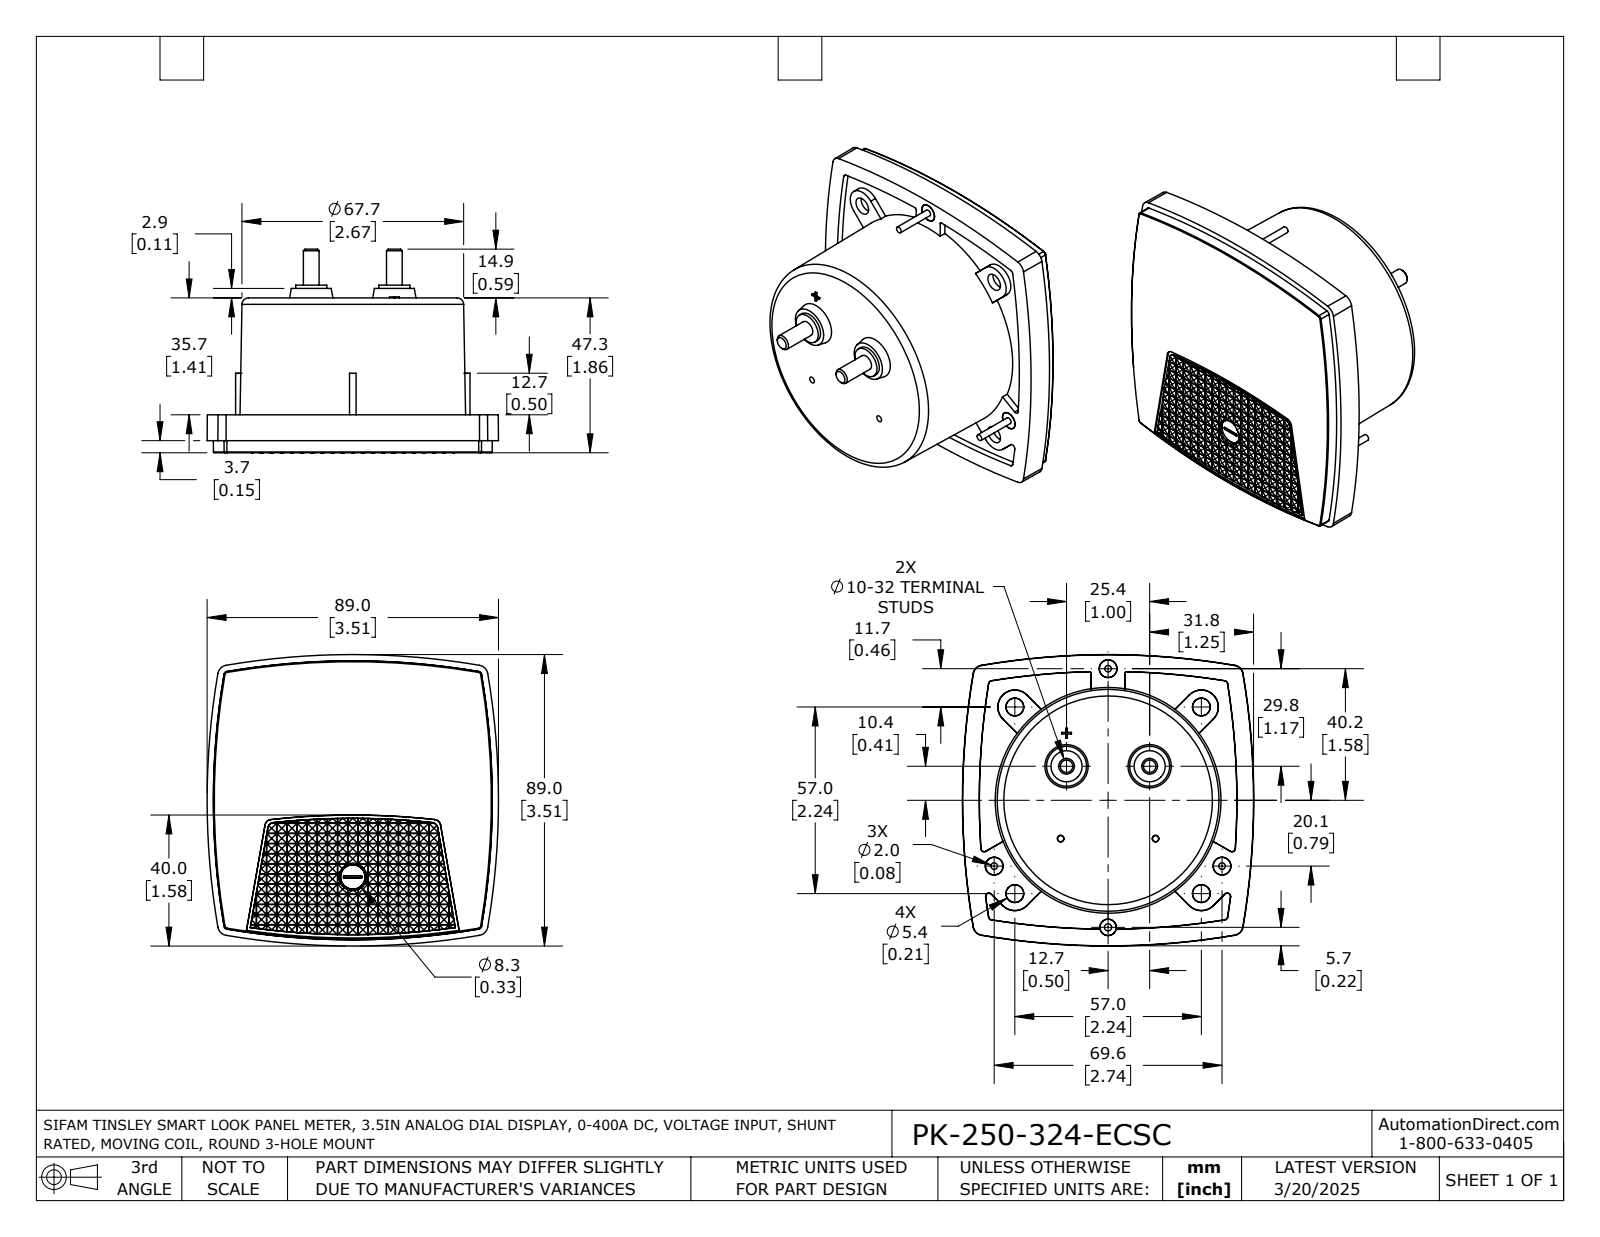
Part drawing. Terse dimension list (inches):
name: PK-250-324-ECSC
written by: SolidWorks 2021 (AUTOMOTIVE_DESIGN)
unit: in
bodies: 1 solid, 1078 faces (950 planar, 23 cylindrical, 105 other)
size: 3.505 × 3.505 × 2.453
volume: 12.99 in³; area: 44.29 in²
holes: 1× ⌀0.087
bosses: 3× ⌀0.213, 3× ⌀0.079, 2× ⌀0.374, 2× ⌀0.189
rounds: 1× R8.961
face distances: 1.862, 1.406, 0.457, 0.079, 1.484, 0.378, 0.024, 0.096, 0.072, 0.12
